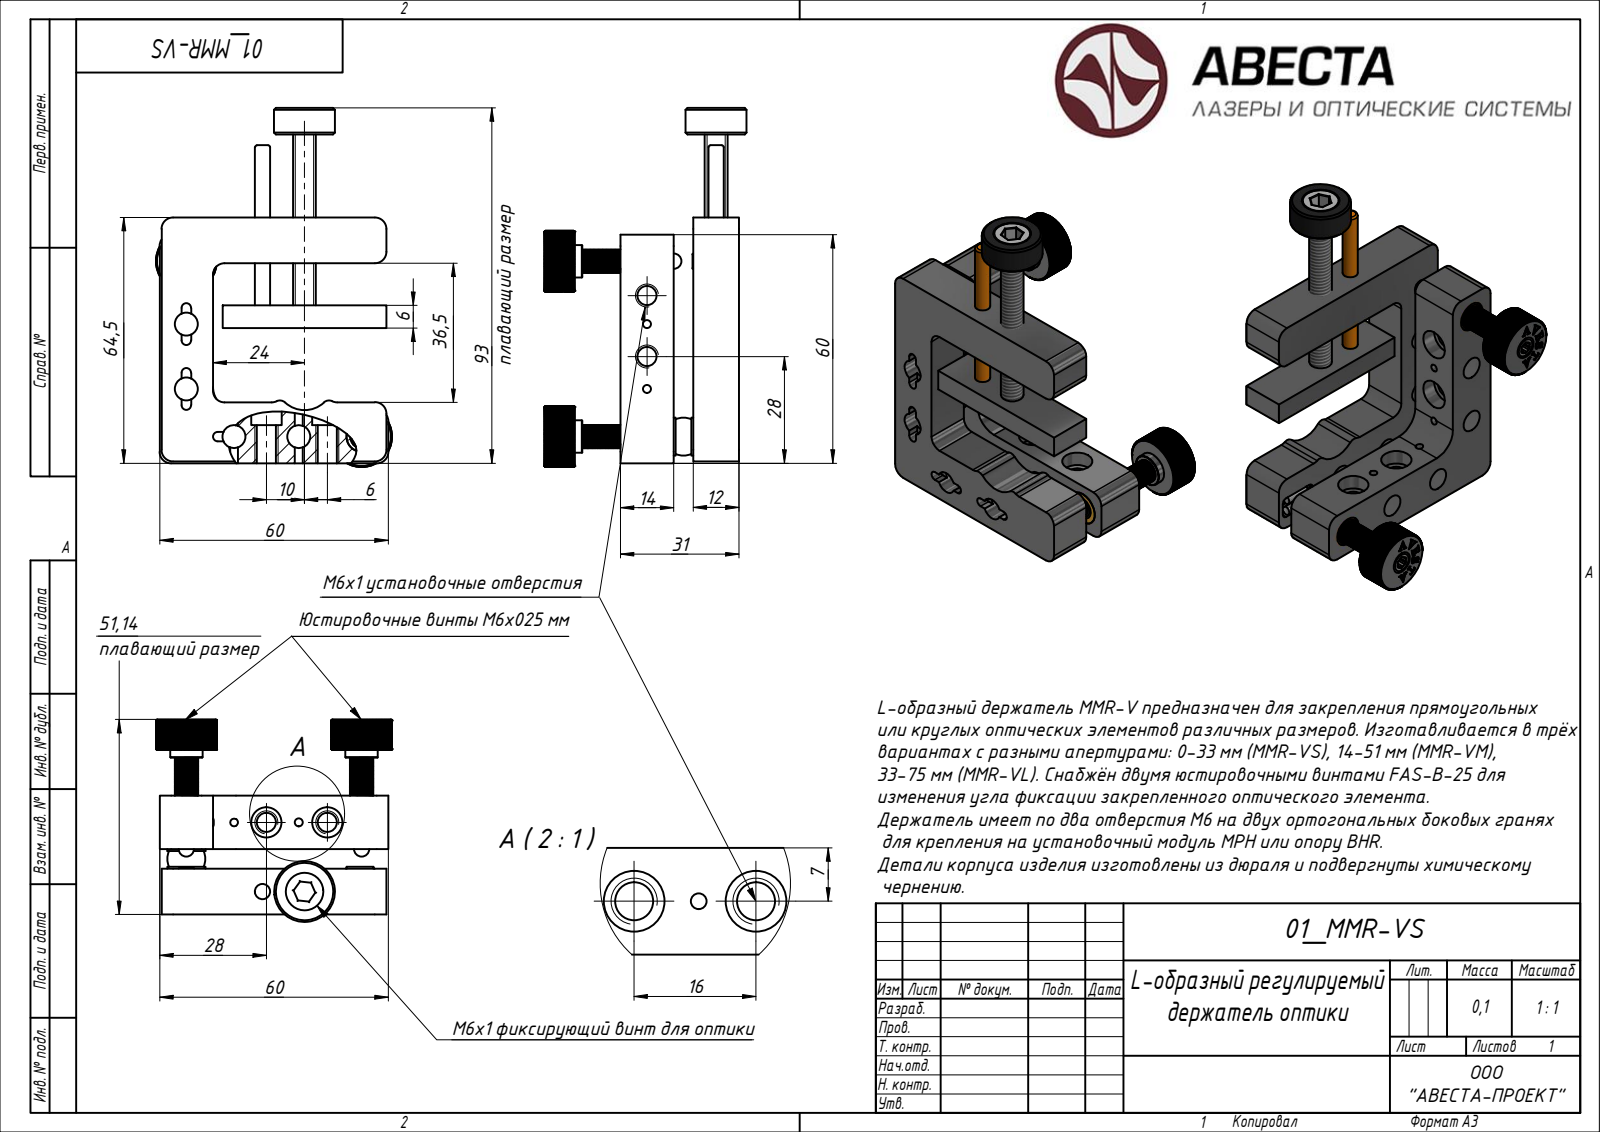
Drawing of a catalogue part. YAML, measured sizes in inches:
step_written_by: "ST-DEVELOPER v15 (AUTOMOTIVE_DESIGN)"
units: inches
bodies: {solids: 18, faces: 718, planar: 323, cylindrical: 0, other: 395}
overall_size: [3.711, 2.441, 1.901]
volume: 3.107
surface_area: 44.64
face_to_face_distances: [0.472, 0.551, 0.02, 0.754, 1.226, 0.202, 0.675, 0.531, 0.236, 2.539]
